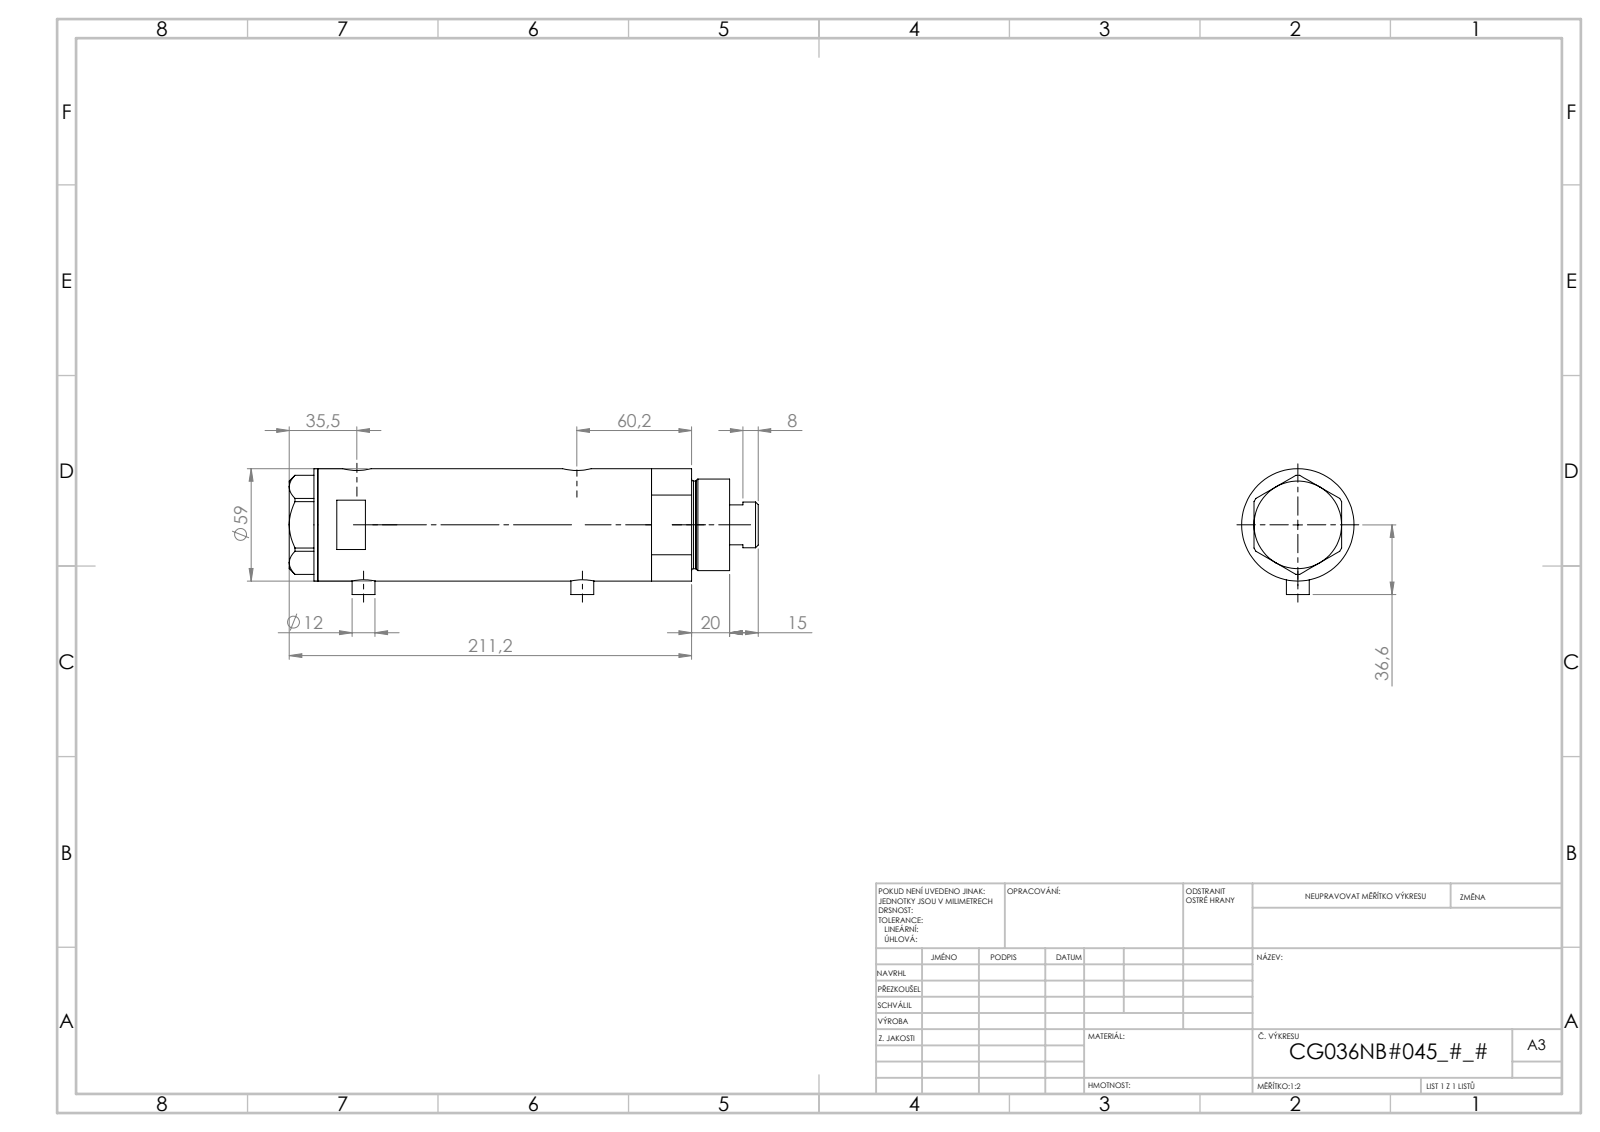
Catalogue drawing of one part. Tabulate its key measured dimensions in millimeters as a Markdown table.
| quantity | value |
| --- | --- |
| part name | V270CG_BACK; V270CG_MIDDLE; V270CG_VC; V270CG_FRONT |
| STEP written by | SolidWorks 2019 (CONFIG_CONTROL_DESIGN) |
| units | millimeters |
| bodies | 4 solids, 126 faces (53 planar, 53 cylindrical, 20 other) |
| overall size | 208.42 × 60.1 × 59 |
| volume | 470 455 mm³ |
| surface area | 98 858 mm² |
| round holes (diameter × count) | 5 × 2, 9.73 × 2, 12.5 × 2, 15 × 2, 8.5 × 1, 25 × 1, 26.5 × 1, 36 × 1, 40 × 1, 52 × 1 |
| round bosses / shafts (diameter × count) | 12 × 2, 59 × 1, 48 × 1, 46 × 1, 24 × 1 |
| main face-to-face distances | 78.85, 15, 117.34, 102.34, 193.42, 38.5, 23.5, 78.84, 38.49, 23.49 |
| hole center spacings | 2.9, 3.5, 77.15, 80.05, 80.65, 83.55, 2.89, 2.91 |
